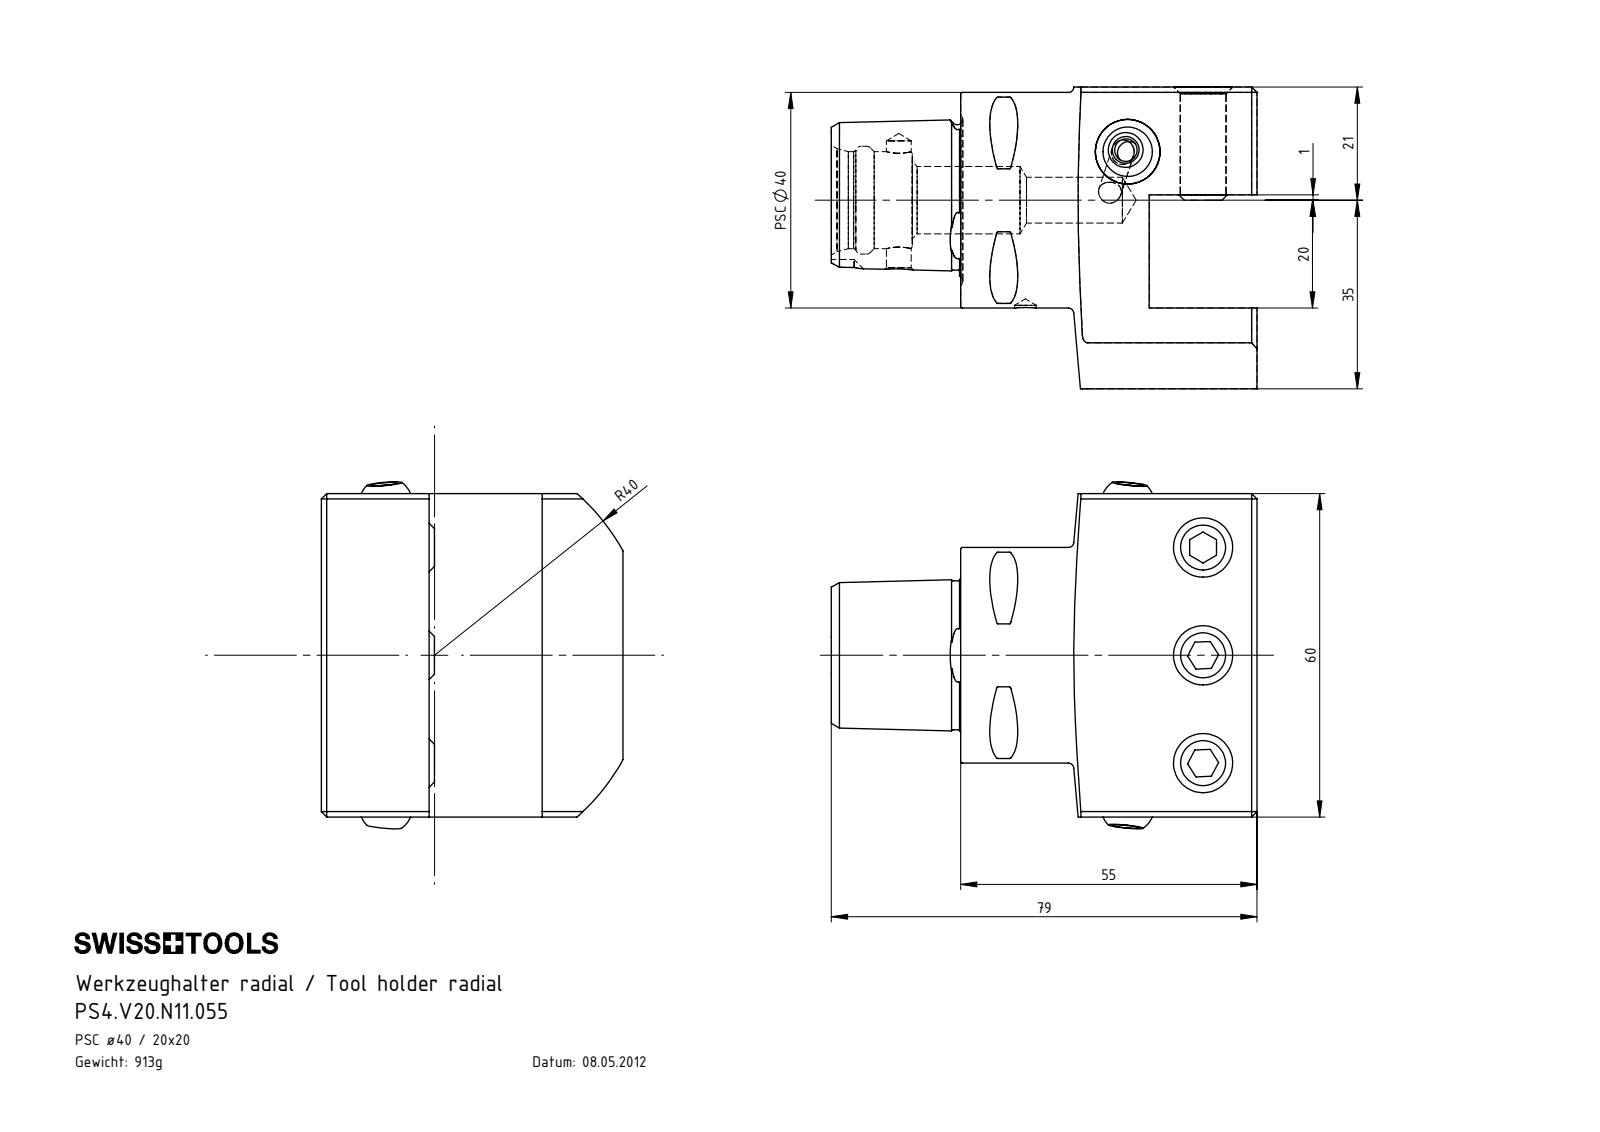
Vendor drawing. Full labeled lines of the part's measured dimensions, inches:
Part name (STEP PRODUCT): KU1-U12.001.010_1; PS4-V20.N11.055_A; KU1-U12.001.010; PS4.V20.N11.055 (+2 more)
STEP written by: SolidWorks 2017 (AUTOMOTIVE_DESIGN)
Units: inches
Bodies: 8 solids, 254 faces (71 planar, 61 cylindrical, 122 other)
Overall size (bounding box): 3.11 × 2.504 × 2.205
Volume: 7.135 in³ · Surface area: 45.01 in²
Round holes (diameter × count): ⌀0.335 ×4, ⌀0.165 ×3, ⌀0.157 ×1, ⌀0.181 ×1, ⌀0.276 ×1, ⌀0.472 ×1, ⌀0.492 ×1, ⌀0.709 ×1, ⌀0.787 ×1
Round bosses / shafts (diameter × count): ⌀0.394 ×3, ⌀1.575 ×1
Partial cylindrical surfaces — rounded edges, fillets, slot ends (radius × count): R0.012 ×8, R0.118 ×1, R1.575 ×1
Main face-to-face distances: 0.787, 0.591, 2.205, 1.614, 0.827, 1.417, 2.362, 1.378, 2.165, 0.315
Hole centre spacings: 0.787, 1.519, 2.36, 0.925, 1.299, 1.575, 2.224
